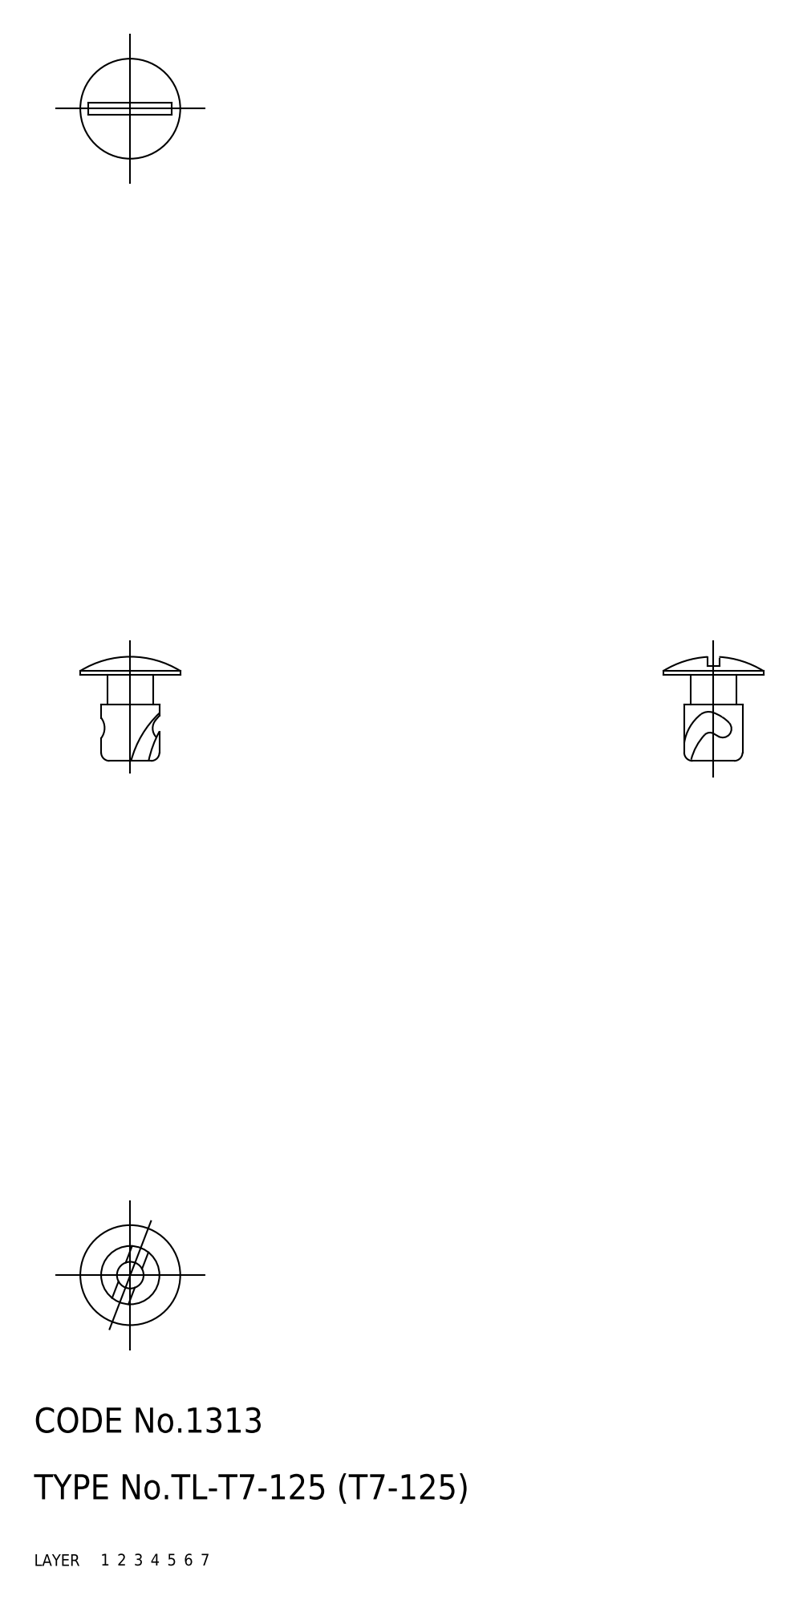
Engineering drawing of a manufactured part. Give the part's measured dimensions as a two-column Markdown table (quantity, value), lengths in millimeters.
| quantity | value |
| --- | --- |
| part name | fastener |
| STEP written by | CADfix (AUTOMOTIVE_DESIGN) |
| units | millimeters |
| bodies | 1 solid, 35 faces (0 planar, 0 cylindrical, 35 other) |
| overall size | 12.48 × 12 × 12 |
| volume | 373 mm³ |
| surface area | 564 mm² |
